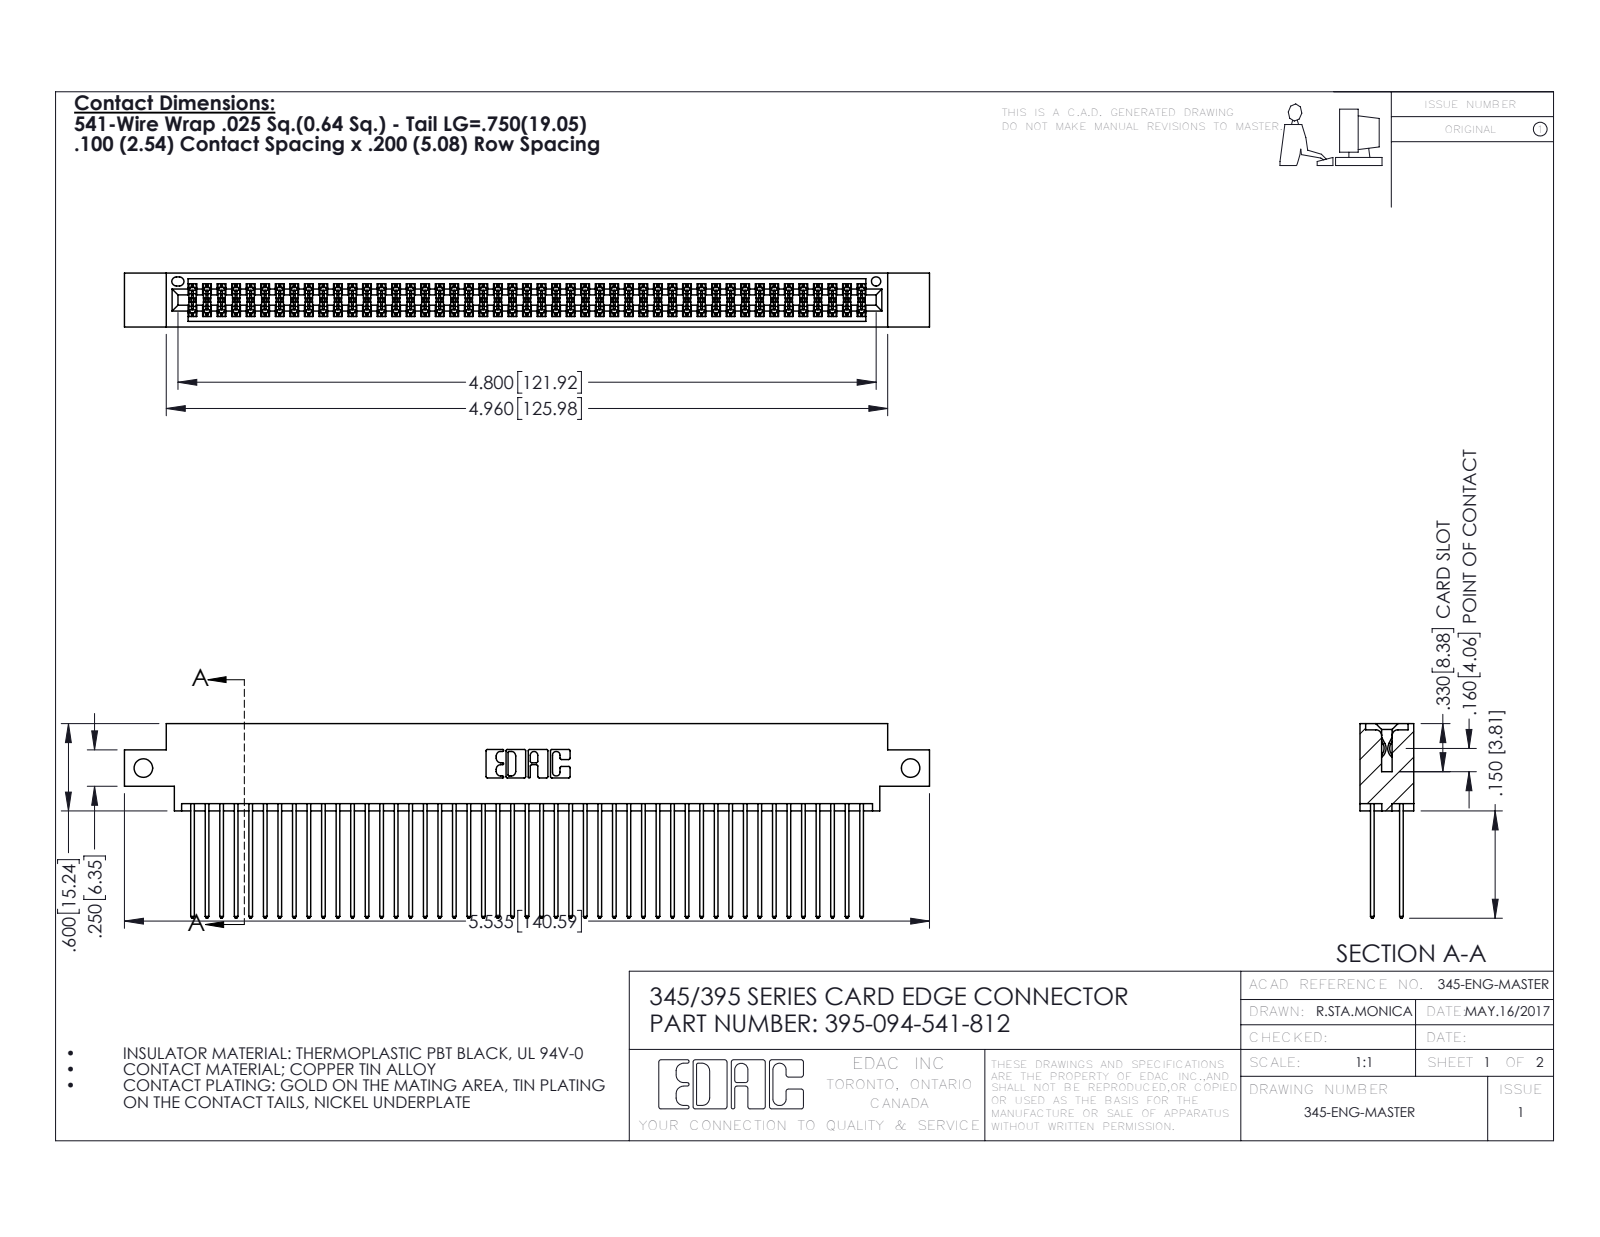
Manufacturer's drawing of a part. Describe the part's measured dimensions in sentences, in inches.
The part is named "345-292-001_345-293-141; 345 Part_0.170 Offset - Side Mount; 395-094-541-812". Its 3-D file was written by "SolidWorks 2016 (CONFIG_CONTROL_DESIGN)". It is 95 solids with 4830 faces: 3186 planar, 1644 cylindrical and 0 other. Overall it measures 5.535 by 1.337 by 0.37 inches. Its volume is 0.857 cubic inches and its surface area 36.26 square inches. Round holes: 2 of diameter 0.128, 1 of diameter 0.064. Partial cylindrical surfaces (rounded edges, fillets, slot ends): 141 of radius 0.006, 94 of radius 0.01, 22 of radius 0.01, 6 of radius 0.007, 6 of radius 0.031, 3 of radius 0.026, 2 of radius 0.014, 2 of radius 0.019. The main face-to-face distances are 0.298, 0.072, 0.2, 0.098, 0.272, 0.025, 0.37, 0.225, 0.175, 0.149. The hole center spacings are 5.275.
